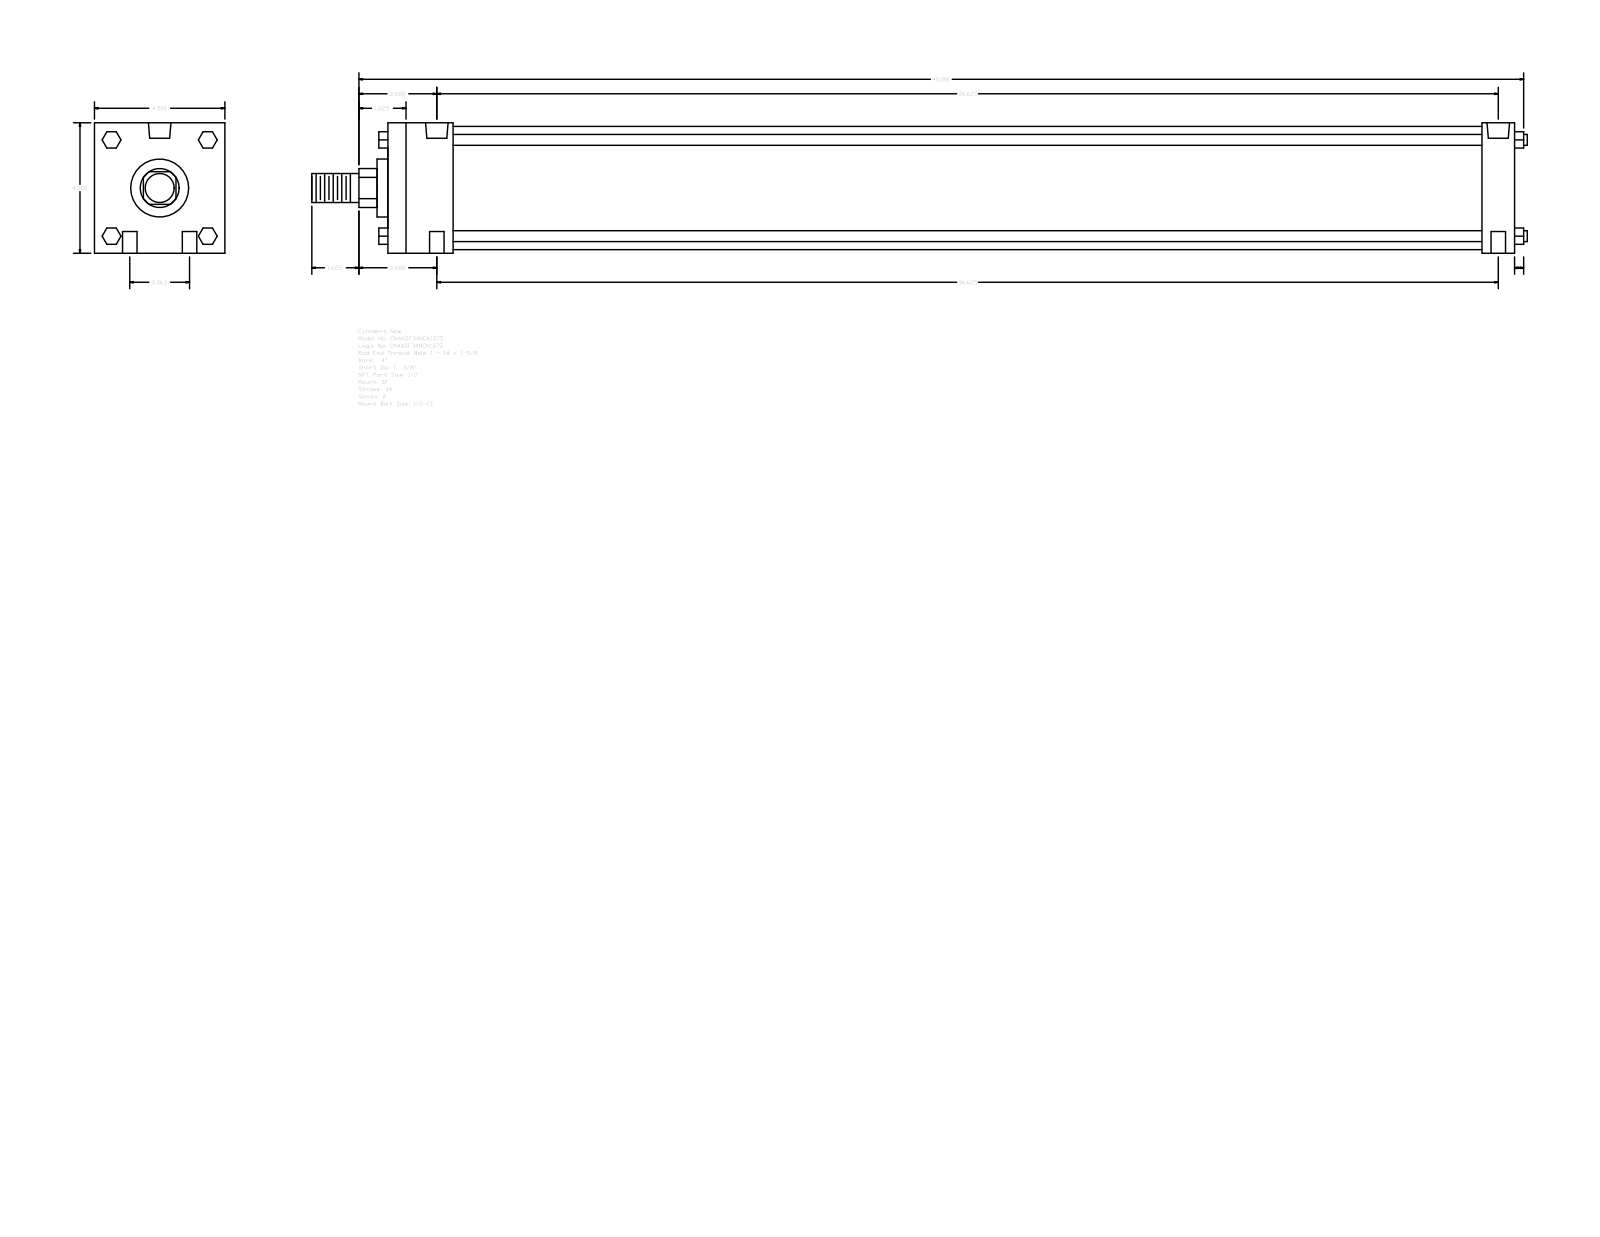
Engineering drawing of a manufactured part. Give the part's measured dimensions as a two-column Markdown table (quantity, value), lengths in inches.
| quantity | value |
| --- | --- |
| part name | A_SF__0400_1.375 |
| STEP written by | GSSL Pune (CONFIG_CONTROL_DESIGN) |
| units | inches |
| bodies | 0 solids, 124 faces (94 planar, 30 cylindrical, 0 other) |
| overall size | 41.937 × 4.5 × 4.5 |
| round holes (diameter × count) | 0.5 × 4, 0.344 × 2, 0.778 × 2 |
| round bosses / shafts (diameter × count) | 0.375 × 4, 4.25 × 1, 2 × 1, 1.375 × 1, 1 × 1 |
| partial cylindrical surfaces (radius × count) | 0.672 × 1 |
| main face-to-face distances | 4.5, 38.875, 2.25, 1.125, 37.75, 35.5, 36.625, 2.625, 0.563, 0.375 |
| hole center spacings | 1.031, 36.64, 36.625, 2.062, 36.683, 36.375 |
